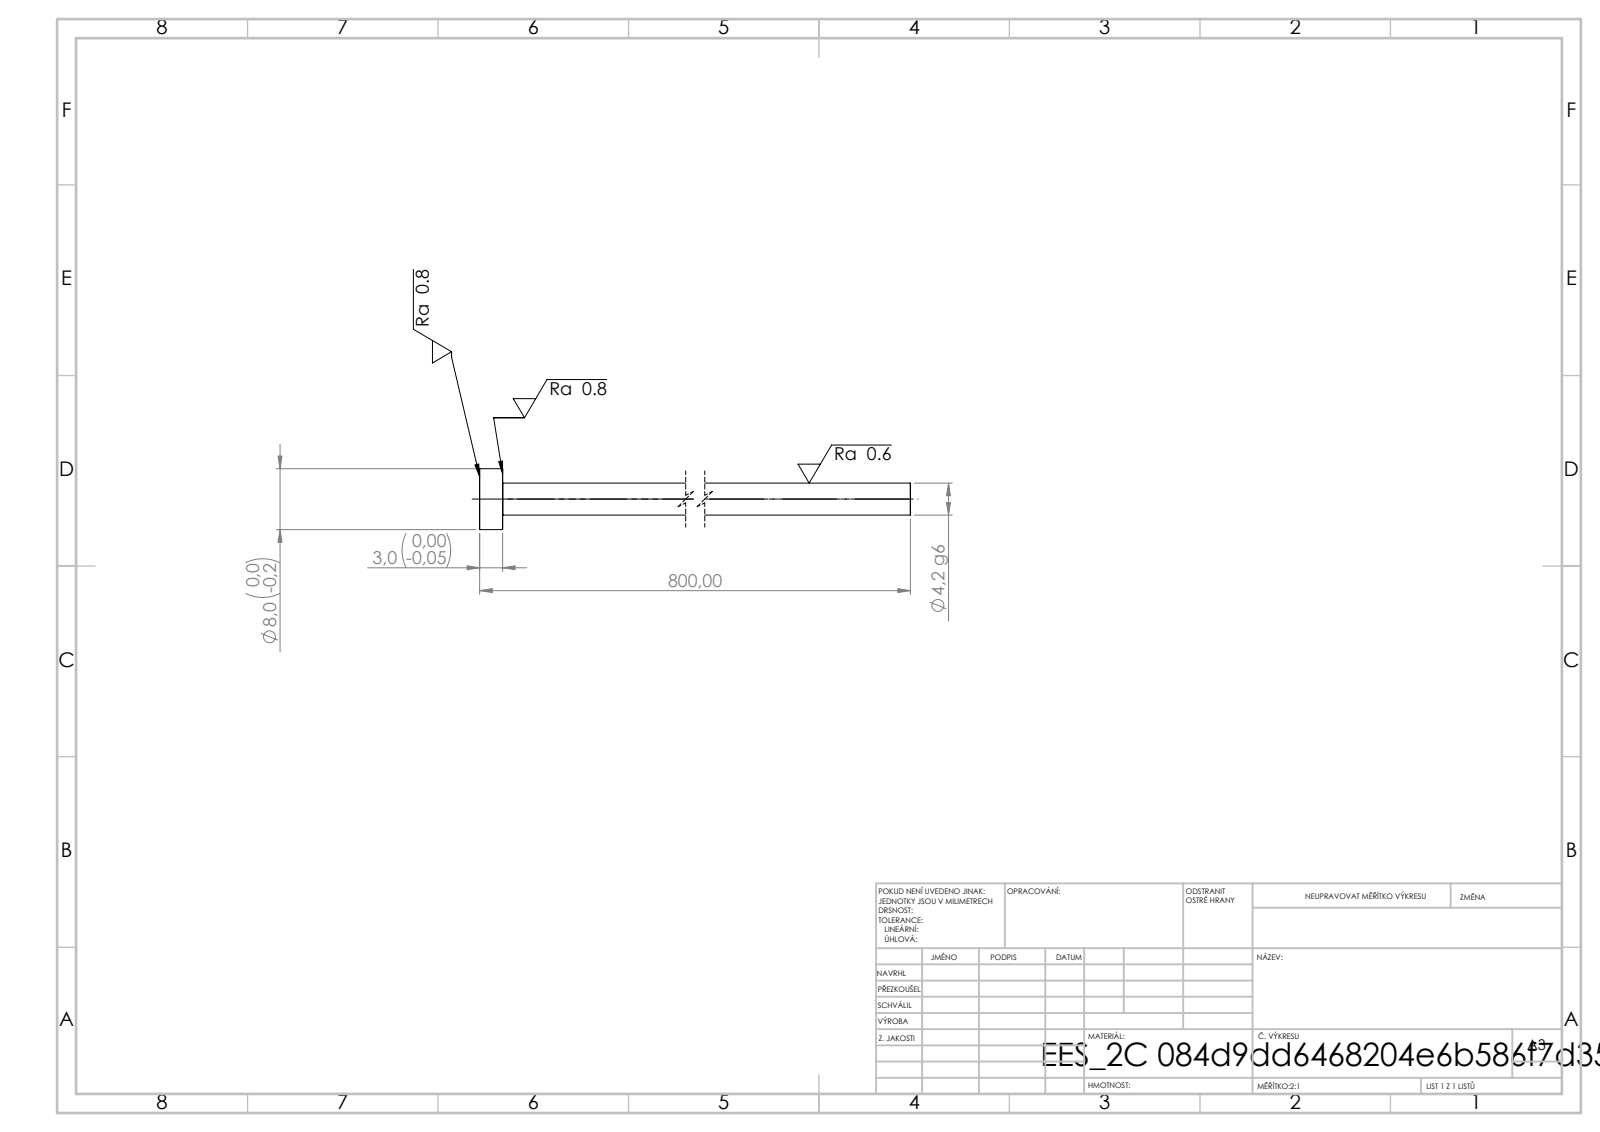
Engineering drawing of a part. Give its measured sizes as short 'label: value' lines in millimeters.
written by: SolidWorks 2019 (CONFIG_CONTROL_DESIGN)
unit: mm
bodies: 1 solid, 7 faces (3 planar, 4 cylindrical, 0 other)
size: 800 × 8 × 8
volume: 11 193 mm³; area: 10 692 mm²
bosses: 1× ⌀8, 1× ⌀4.2
face distances: 3, 800, 797
